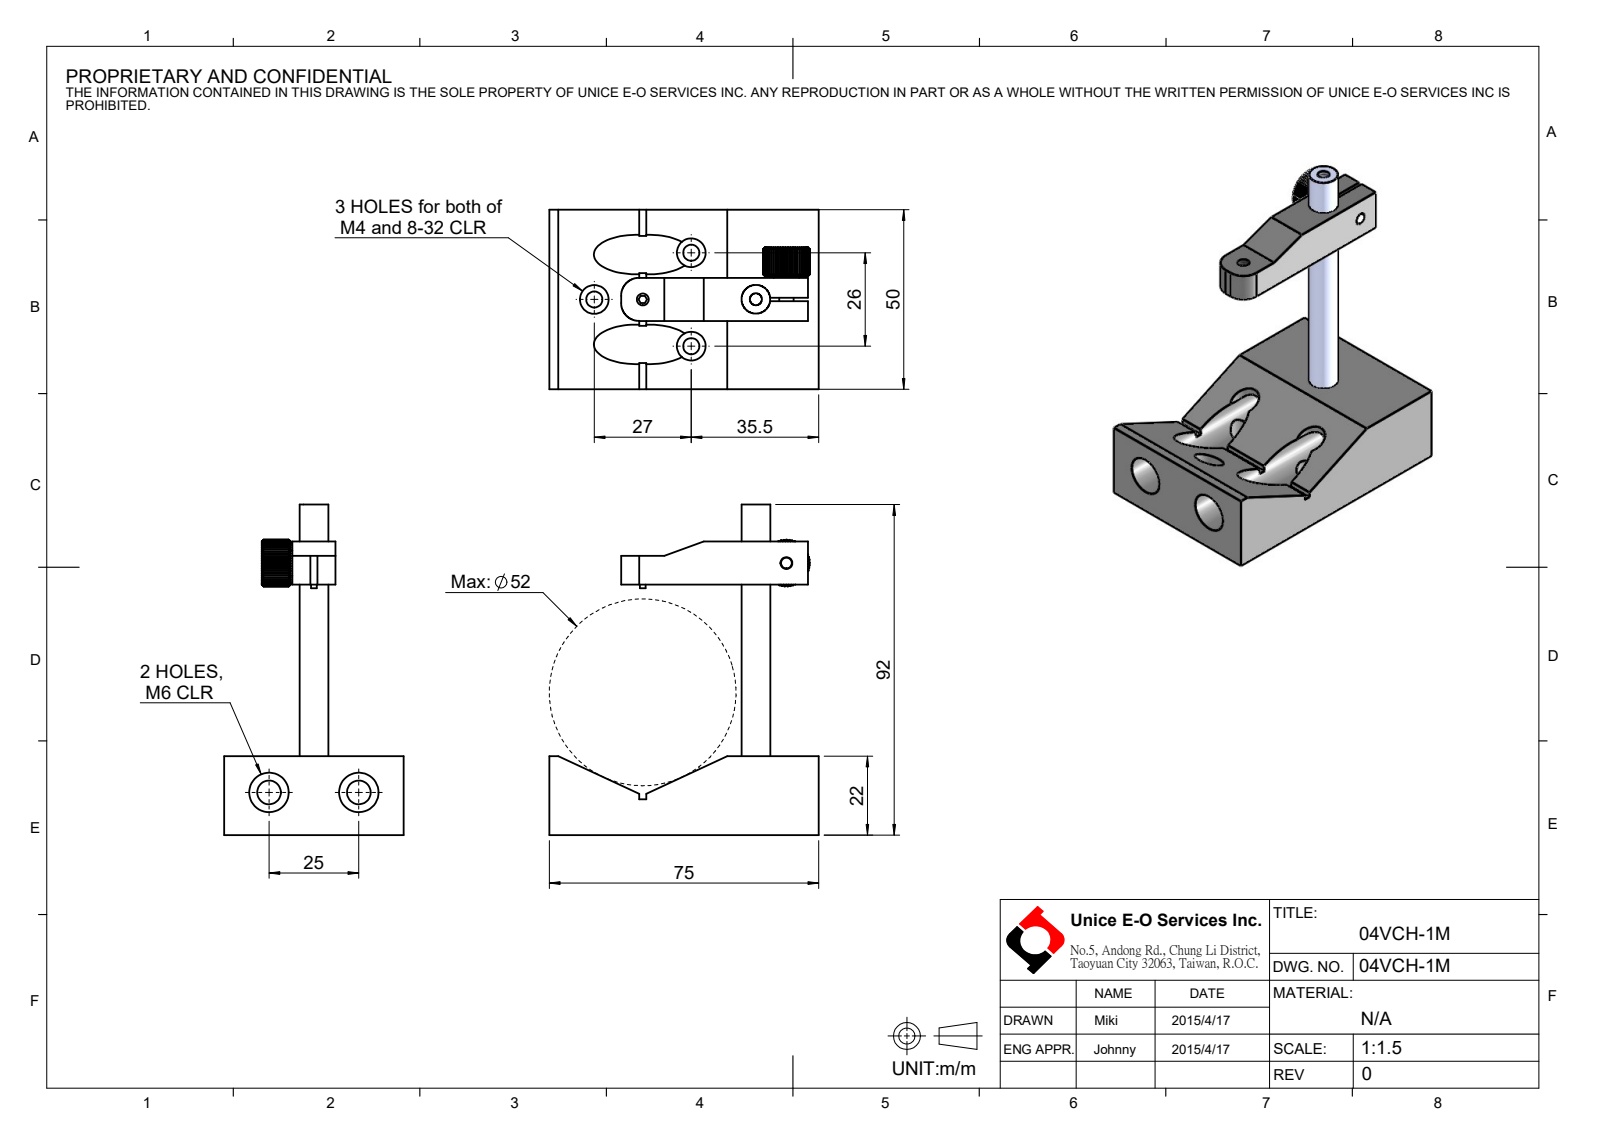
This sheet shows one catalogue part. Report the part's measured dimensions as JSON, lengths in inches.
{"part_name": "04VCH-1M", "step_written_by": "SolidWorks 2016 (CONFIG_CONTROL_DESIGN)", "units": "inches", "bodies": {"solids": 8, "faces": 411, "planar": 169, "cylindrical": 120, "other": 122}, "overall_size": [3.622, 2.953, 1.969], "volume_in3": 4.052, "surface_area_in2": 37.04, "round_holes": [[0.177, 5], [0.315, 4], [0.13, 3], [0.26, 2], [0.433, 2], [0.059, 1], [0.161, 1], [0.283, 1]], "round_bosses_or_shafts": [[0.157, 2], [0.276, 1], [0.063, 1]], "partial_cylinders_radius": [[0.197, 2], [0.256, 1]], "face_to_face_distances": [1.969, 0.866, 1.22, 0.748, 2.953, 0.472, 2.745, 1.879, 2.352, 3.218], "hole_center_spacings": [0.738, 0.874, 1.18, 0.531, 0.984, 1.024, 1.24, 1.772]}
